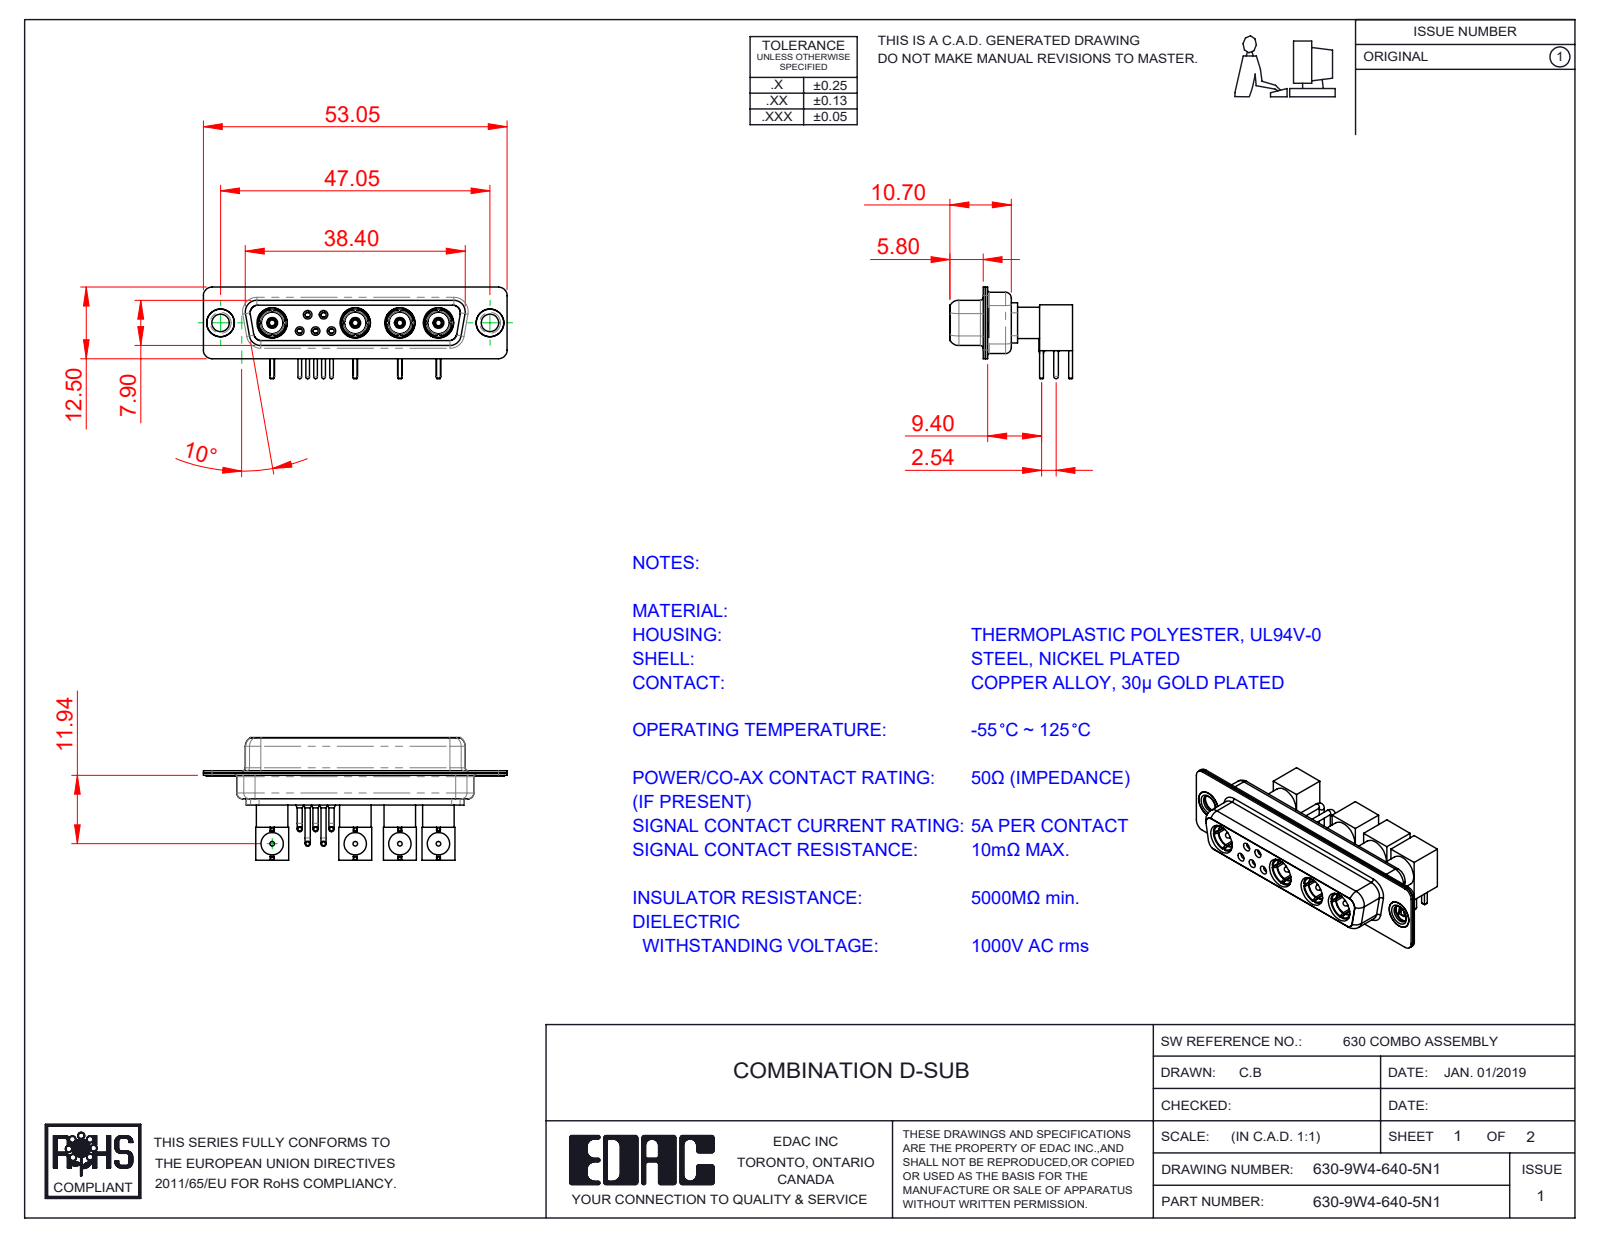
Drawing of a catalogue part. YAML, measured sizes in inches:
part_name: "Co-Ax Plug Assy_RA; 630Combo Housing_9W4; Co-Ax Plug_RA PC Tail; Pin_RA (+8 more)"
step_written_by: "SolidWorks 2020 (CONFIG_CONTROL_DESIGN)"
units: inches
bodies: {solids: 34, faces: 1190, planar: 410, cylindrical: 496, other: 284}
overall_size: [2.089, 0.843, 0.63]
volume: 0.281
surface_area: 17.34
round_holes:
  - {diameter: 0.043, count: 9}
  - {diameter: 0.059, count: 9}
  - {diameter: 0.191, count: 6}
  - {diameter: 0.035, count: 5}
  - {diameter: 0.079, count: 5}
  - {diameter: 0.031, count: 4}
  - {diameter: 0.111, count: 4}
  - {diameter: 0.122, count: 4}
  - {diameter: 0.13, count: 4}
  - {diameter: 0.154, count: 4}
  - {diameter: 0.154, count: 4}
  - {diameter: 0.161, count: 4}
round_bosses_or_shafts:
  - {diameter: 0.197, count: 6}
  - {diameter: 0.035, count: 5}
  - {diameter: 0.031, count: 5}
  - {diameter: 0.026, count: 5}
  - {diameter: 0.217, count: 4}
  - {diameter: 0.205, count: 4}
  - {diameter: 0.187, count: 4}
  - {diameter: 0.163, count: 4}
partial_cylinders:
  - {radius: 0.059, count: 16}
  - {radius: 0.079, count: 12}
  - {radius: 0.053, count: 8}
  - {radius: 0.063, count: 8}
  - {radius: 0.01, count: 4}
  - {radius: 0.02, count: 4}
  - {radius: 0.024, count: 4}
  - {radius: 0.026, count: 4}
face_to_face_distances: [0.016, 0.018, 0.071, 0.055, 0.333, 0.35, 0.244, 0.073, 0.278, 0.031]
hole_center_spacings: [0.124, 0.265, 0.307, 0.571, 0.572, 0.572, 0.878, 1.143]
